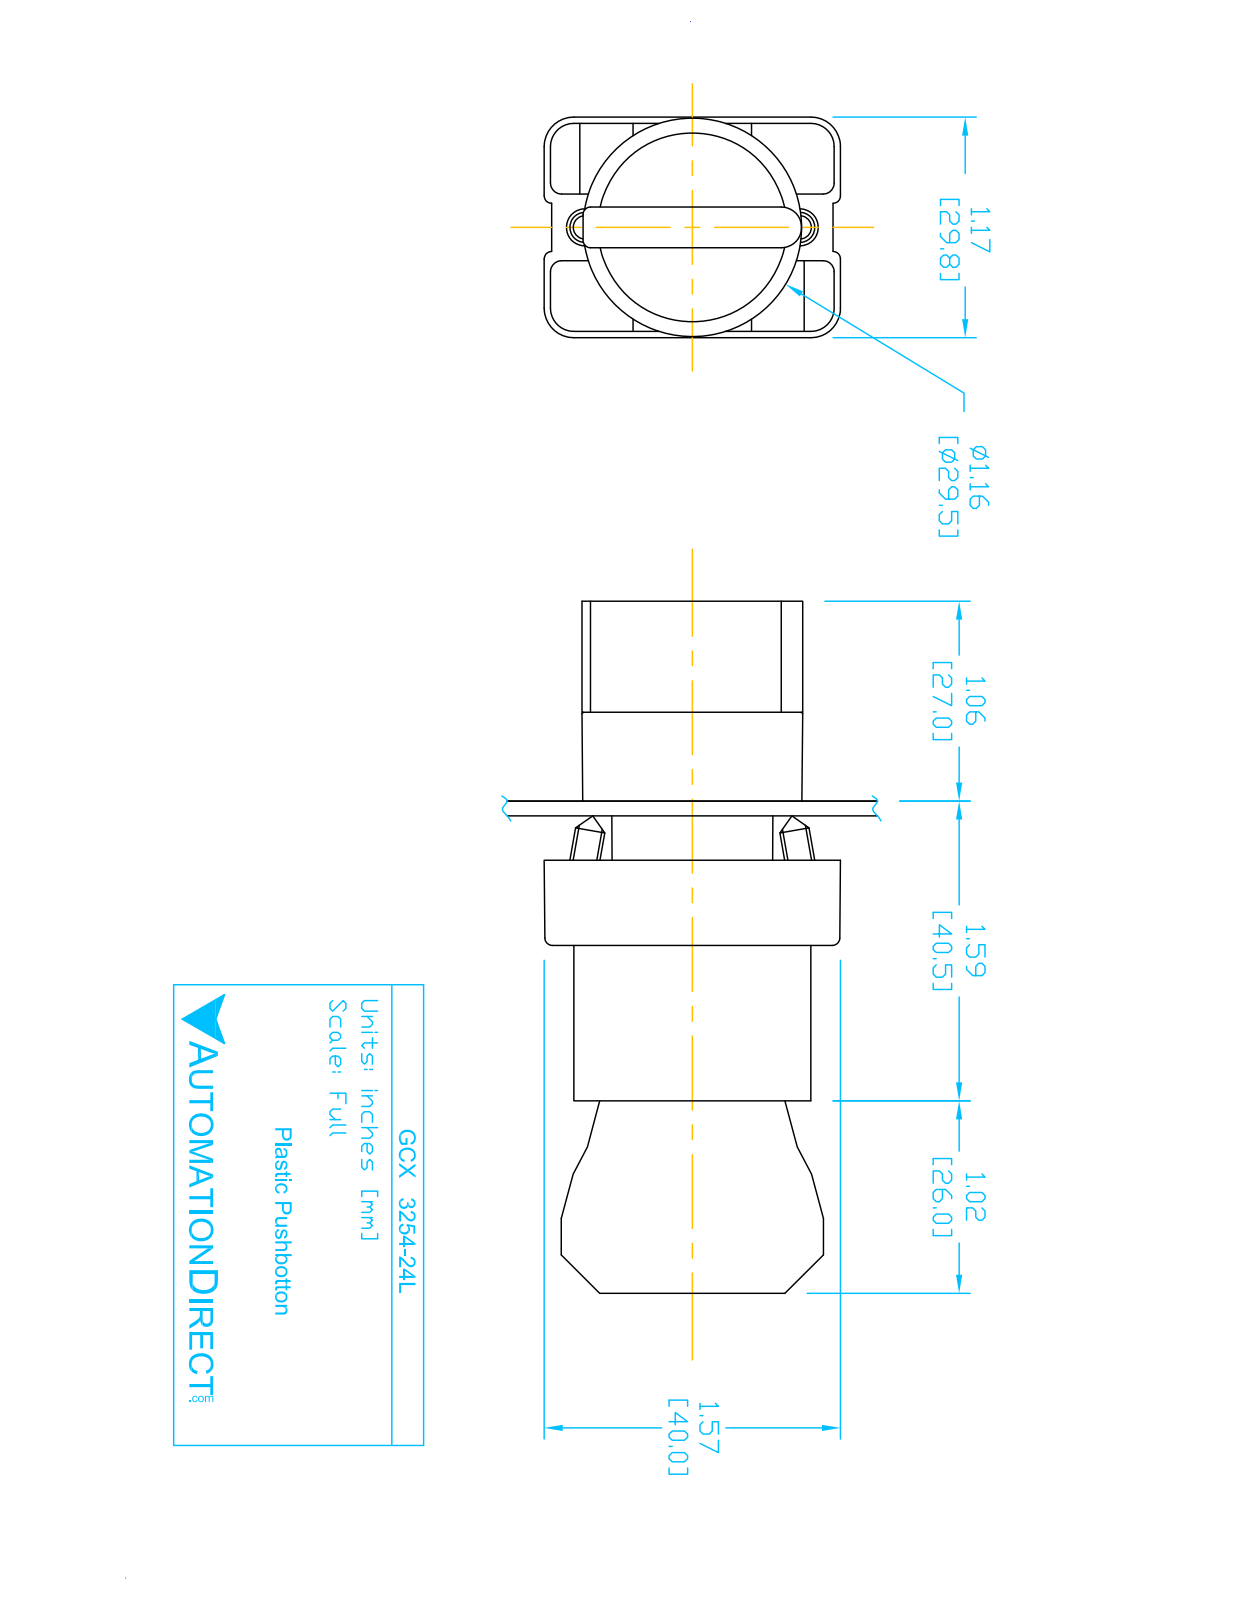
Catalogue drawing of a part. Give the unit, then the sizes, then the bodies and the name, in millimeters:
Units: millimetres
Overall size (bounding box): 92.8 × 40.2 × 29.9
Round holes (diameter × count): ⌀2 ×2, ⌀3.1 ×2, ⌀3.3 ×2, ⌀2.2 ×1, ⌀5 ×1, ⌀11.9 ×1, ⌀22.3 ×1, ⌀22.6 ×1, ⌀26 ×1
Round bosses / shafts (diameter × count): ⌀4 ×4, ⌀29.8 ×1, ⌀25.5 ×1, ⌀24 ×1, ⌀21.7 ×1, ⌀19.8 ×1, ⌀12.8 ×1
Partial cylindrical surfaces — rounded edges, fillets, slot ends (radius × count): R1.5 ×24, R1 ×12, R3.1 ×12, R4 ×12, R1 ×9, R3.3 ×2, R0.5 ×1, R1.6 ×1
Main face-to-face distances: 21, 51.3, 30.3, 14.7, 31.6, 29.7, 12, 11.9, 0.8, 0.8
Hole centre spacings: 6, 13.8, 12, 12.4
Volume: 45 870 mm³ · Surface area: 25 160 mm²
Bodies: 8 solids, 445 faces (263 planar, 151 cylindrical, 31 other)
Part name (STEP PRODUCT): ECX1050; GCX3254L OPERATOR; GCX3254-24L; ECX3029-2 (+1 more)
STEP written by: SolidWorks 2016 (AUTOMOTIVE_DESIGN)
